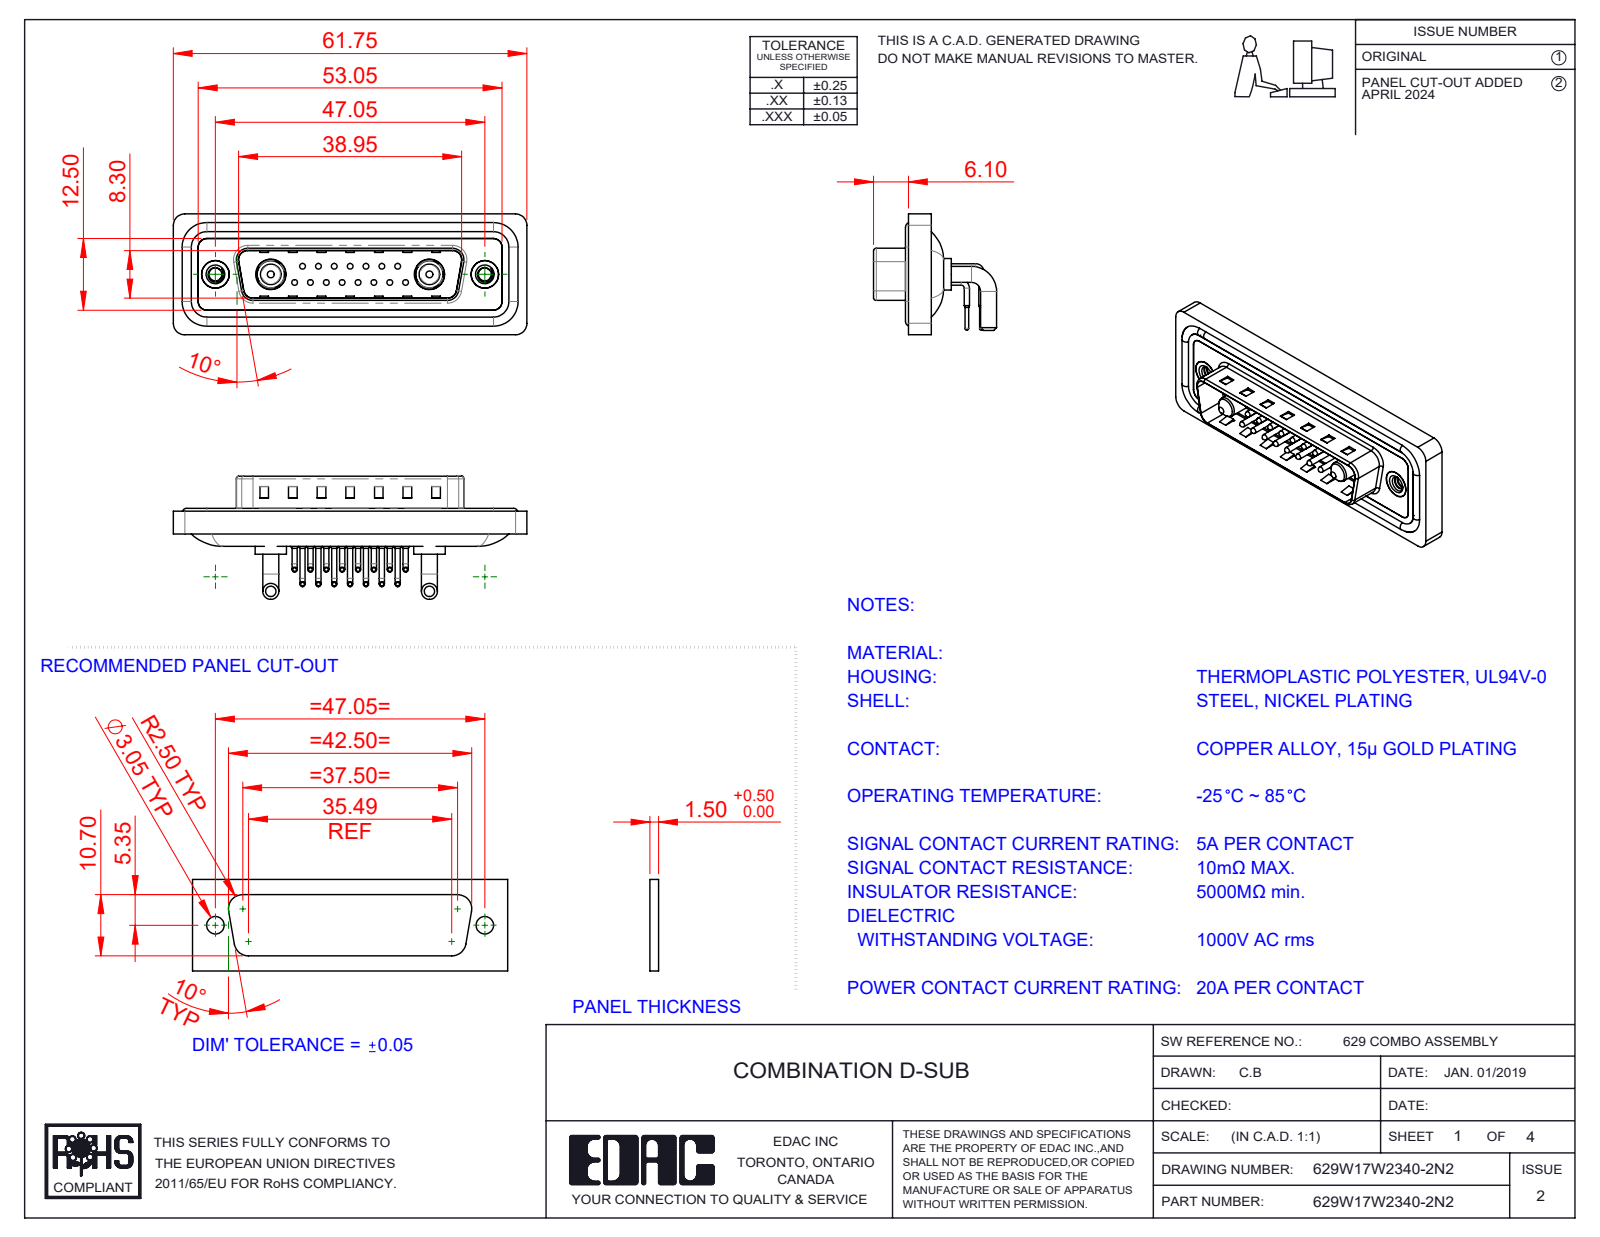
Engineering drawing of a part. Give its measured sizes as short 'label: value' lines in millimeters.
name: 629Combo Contact Row 1; Power Pin_20A RA; 629Combo Waterproof Housing_25 Contacts; 629Combo Shell Front_25 Contacts (+5 more)
written by: SolidWorks 2023 (CONFIG_CONTROL_DESIGN)
unit: mm
bodies: 26 solids, 2219 faces (1189 planar, 770 cylindrical, 260 other)
size: 61.75 × 21.5 × 21.1
volume: 7 523 mm³; area: 12 601 mm²
holes: 15× ⌀0.75, 15× ⌀1.6, 15× ⌀2, 2× ⌀2.26, 2× ⌀4, 2× ⌀4.8, 2× ⌀4.85, 2× ⌀5, 2× ⌀5.3
bosses: 30× ⌀0.9, 15× ⌀1.5, 15× ⌀1, 15× ⌀0.65, 4× ⌀2.8, 4× ⌀1.6, 2× ⌀5.5, 2× ⌀5.2
rounds: 18× R1.5, 18× R2, 15× R1.01, 8× R0.5, 8× R1.6, 4× R0.25, 4× R0.6, 4× R0.65
face distances: 0.4, 2.9, 0.8, 4.1, 1.1, 2.1, 1.6, 4.5, 1.5, 2.5
hole spacings: 3.16, 2.77, 5.54, 8.31, 5.04, 7.49, 11.08, 5.03
